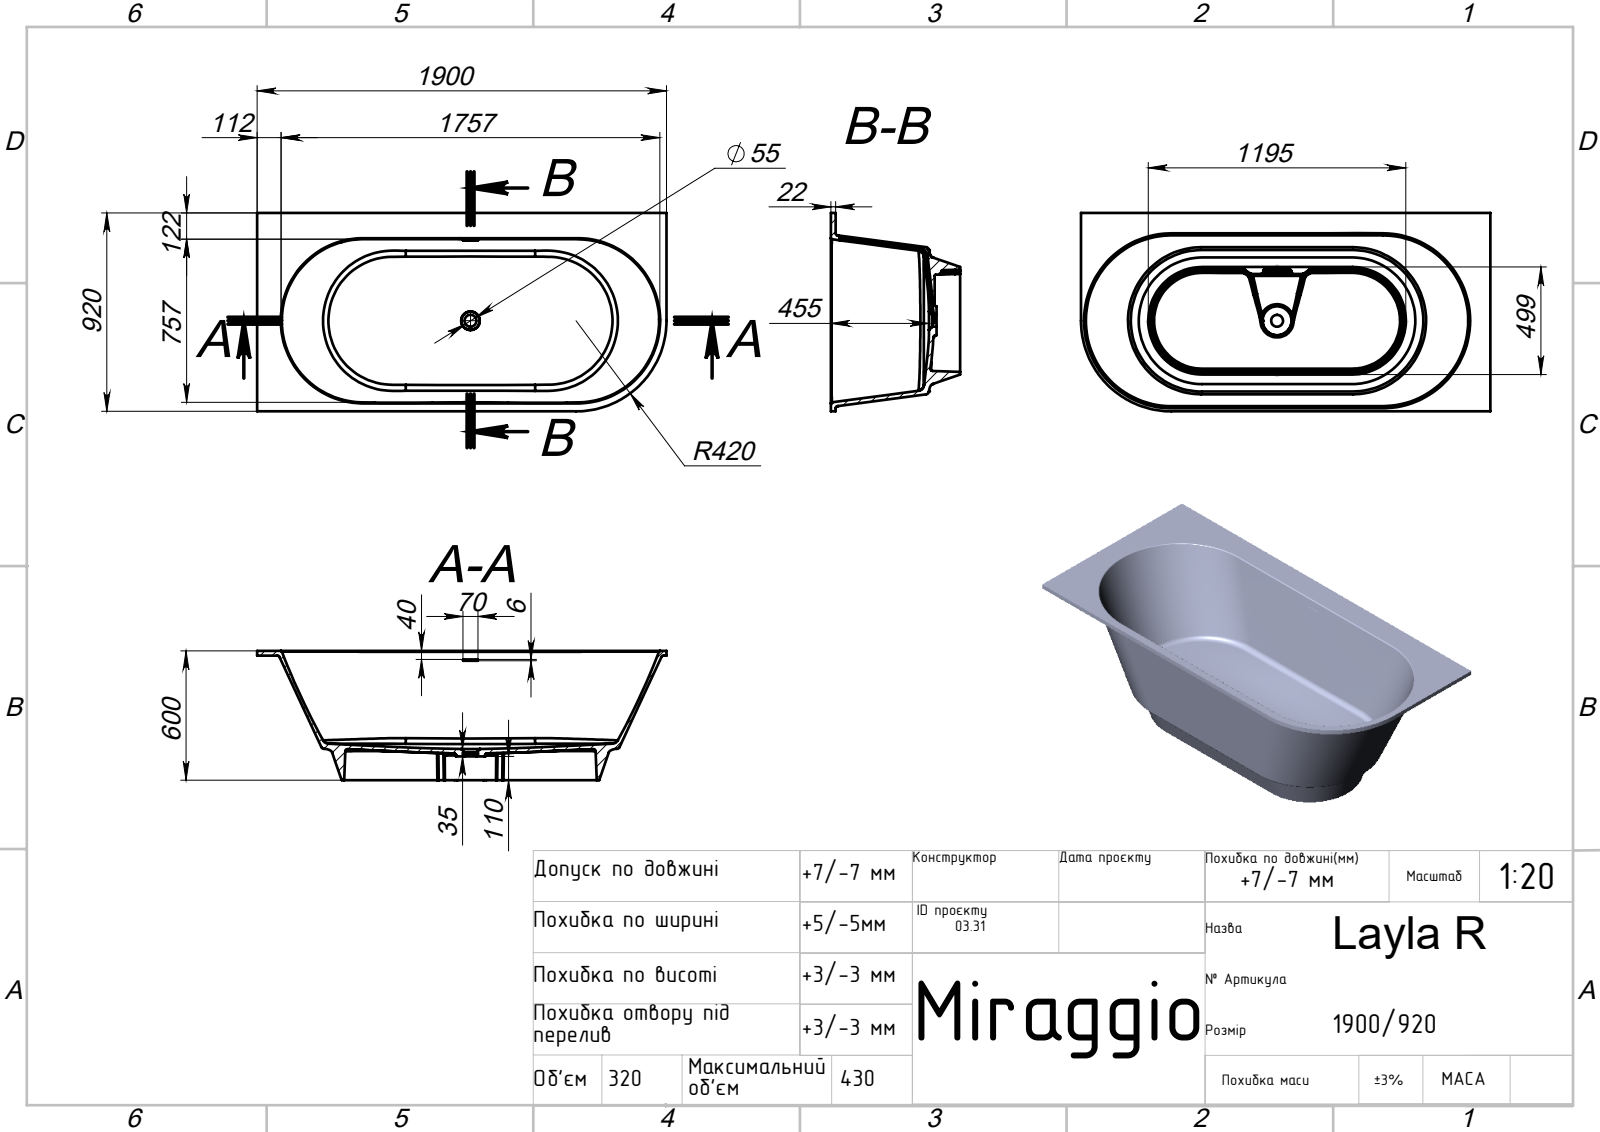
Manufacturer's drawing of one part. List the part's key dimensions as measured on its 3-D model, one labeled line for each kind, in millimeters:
Part name (STEP PRODUCT): Layla R
STEP written by: SolidWorks 2020 (AUTOMOTIVE_DESIGN)
Units: millimetres
Bodies: 1 solid, 111 faces (28 planar, 18 cylindrical, 65 other)
Overall size (bounding box): 1900 × 920 × 600
Volume: 83 250 000 mm³ · Surface area: 6 978 000 mm²
Round holes (diameter × count): ⌀55 ×1
Partial cylindrical surfaces — rounded edges, fillets, slot ends (radius × count): R10 ×4, R5 ×3, R3 ×2, R37 ×1, R46 ×1, R62.5 ×1, R198.58 ×1, R237.27 ×1
Main face-to-face distances: 22, 578, 600, 920, 119, 459, 481, 110, 9, 468
